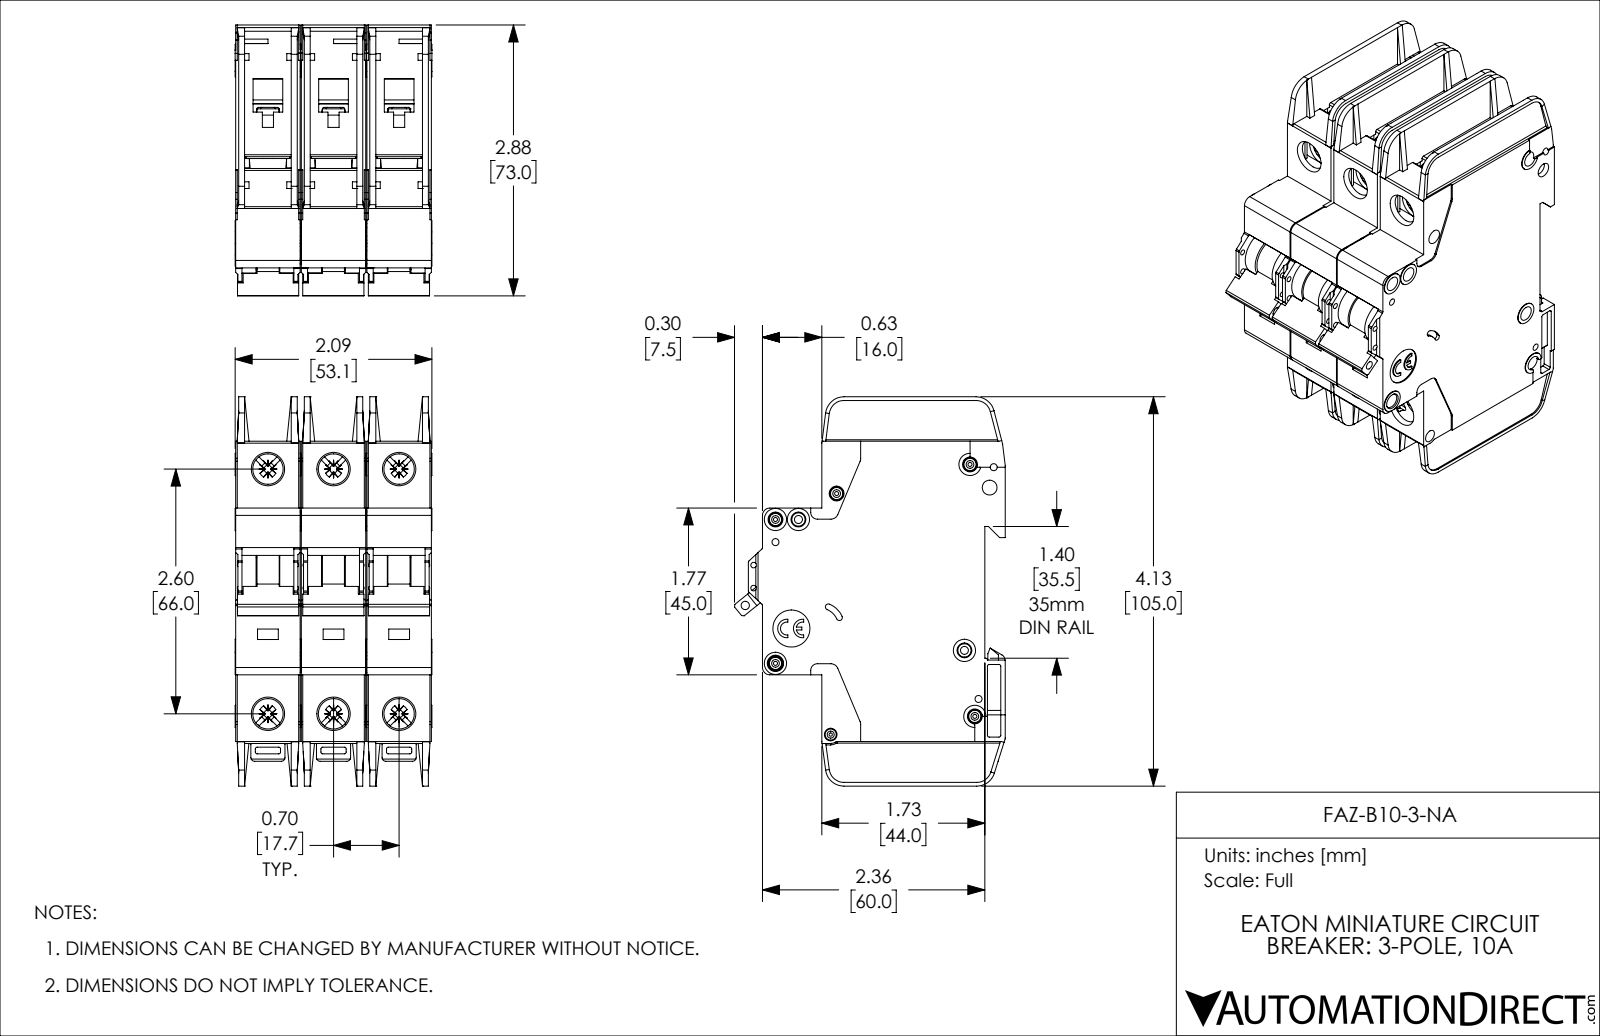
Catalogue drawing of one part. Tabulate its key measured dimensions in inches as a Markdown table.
| quantity | value |
| --- | --- |
| part name | FAZ-B10-3-NA |
| STEP written by | SolidWorks 2019 (AUTOMOTIVE_DESIGN) |
| units | inches |
| bodies | 3 solids, 3381 faces (2013 planar, 1071 cylindrical, 297 other) |
| overall size | 4.134 × 2.876 × 2.091 |
| volume | 14.05 in³ |
| surface area | 123 in² |
| round holes (diameter × count) | 0.157 × 8, 0.323 × 6, 0.043 × 5, 0.075 × 4, 0.059 × 2, 0.085 × 2, 0.035 × 1, 0.089 × 1, 0.098 × 1, 0.134 × 1, 0.394 × 1 |
| round bosses / shafts (diameter × count) | 0.13 × 5, 0.236 × 4, 0.118 × 4, 0.098 × 3 |
| partial cylindrical surfaces (radius × count) | 0.02 × 72, 0.016 × 30, 0.039 × 18, 0.043 × 12, 0.079 × 12, 0.008 × 6, 0.01 × 6, 0.028 × 6 |
| main face-to-face distances | 0.697, 0.047, 1.394, 0.685, 0.591, 1.382, 0.744, 0.65, 0.106, 0.094 |
| hole center spacings | 0.697, 2.69, 2.598, 0.244, 0.537, 0.87, 1.394, 2.948 |
